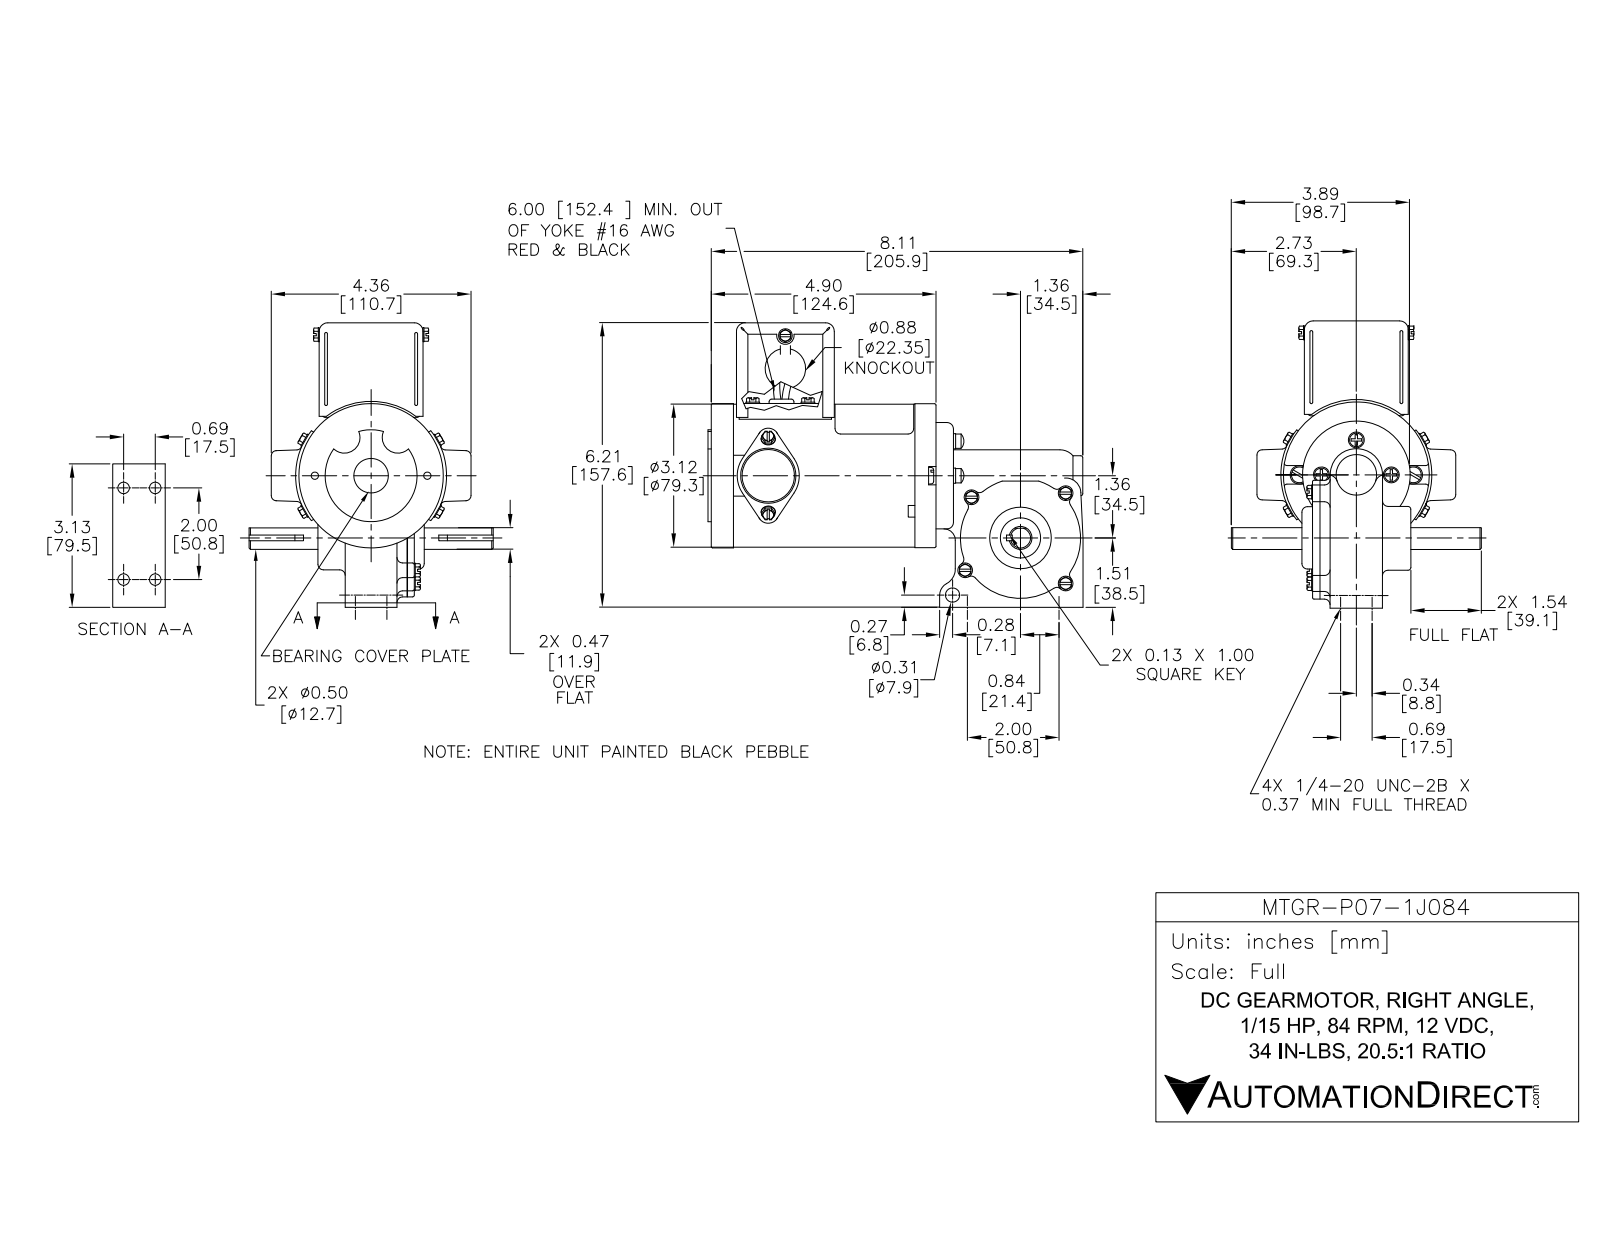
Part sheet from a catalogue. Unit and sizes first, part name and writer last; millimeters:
Units: millimetres
Overall size (bounding box): 207.7 × 159.4 × 138.5
Round holes (diameter × count): ⌀6.4 ×5, ⌀2.4 ×2, ⌀5 ×2, ⌀7.6 ×1, ⌀7.6 ×1, ⌀9.5 ×1, ⌀12.7 ×1, ⌀21.8 ×1, ⌀31.1 ×1, ⌀76.2 ×1, ⌀79.4 ×1
Round bosses / shafts (diameter × count): ⌀8.2 ×4, ⌀7.6 ×4, ⌀8.8 ×3, ⌀7.5 ×3, ⌀3.2 ×2, ⌀2.5 ×2, ⌀80.2 ×1, ⌀79.8 ×1
Partial cylindrical surfaces — rounded edges, fillets, slot ends (radius × count): R2.5 ×10, R4.9 ×4, R5.9 ×4, R3.8 ×2, R4 ×2, R8.7 ×2, R6.4 ×1, R8.6 ×1
Main face-to-face distances: 0.8, 6.4, 1.6, 118.1, 54.2, 7.8, 52, 42.4, 40.8, 6.2
Hole centre spacings: 8.7, 11.6, 17.4, 31.2, 50.8, 51.5, 53.7, 59.1
Volume: 448 500 mm³ · Surface area: 191 700 mm²
Bodies: 40 solids, 712 faces (436 planar, 210 cylindrical, 66 other)
Part name (STEP PRODUCT): P07-1J084
STEP written by: SolidWorks 2013 (AUTOMOTIVE_DESIGN)
